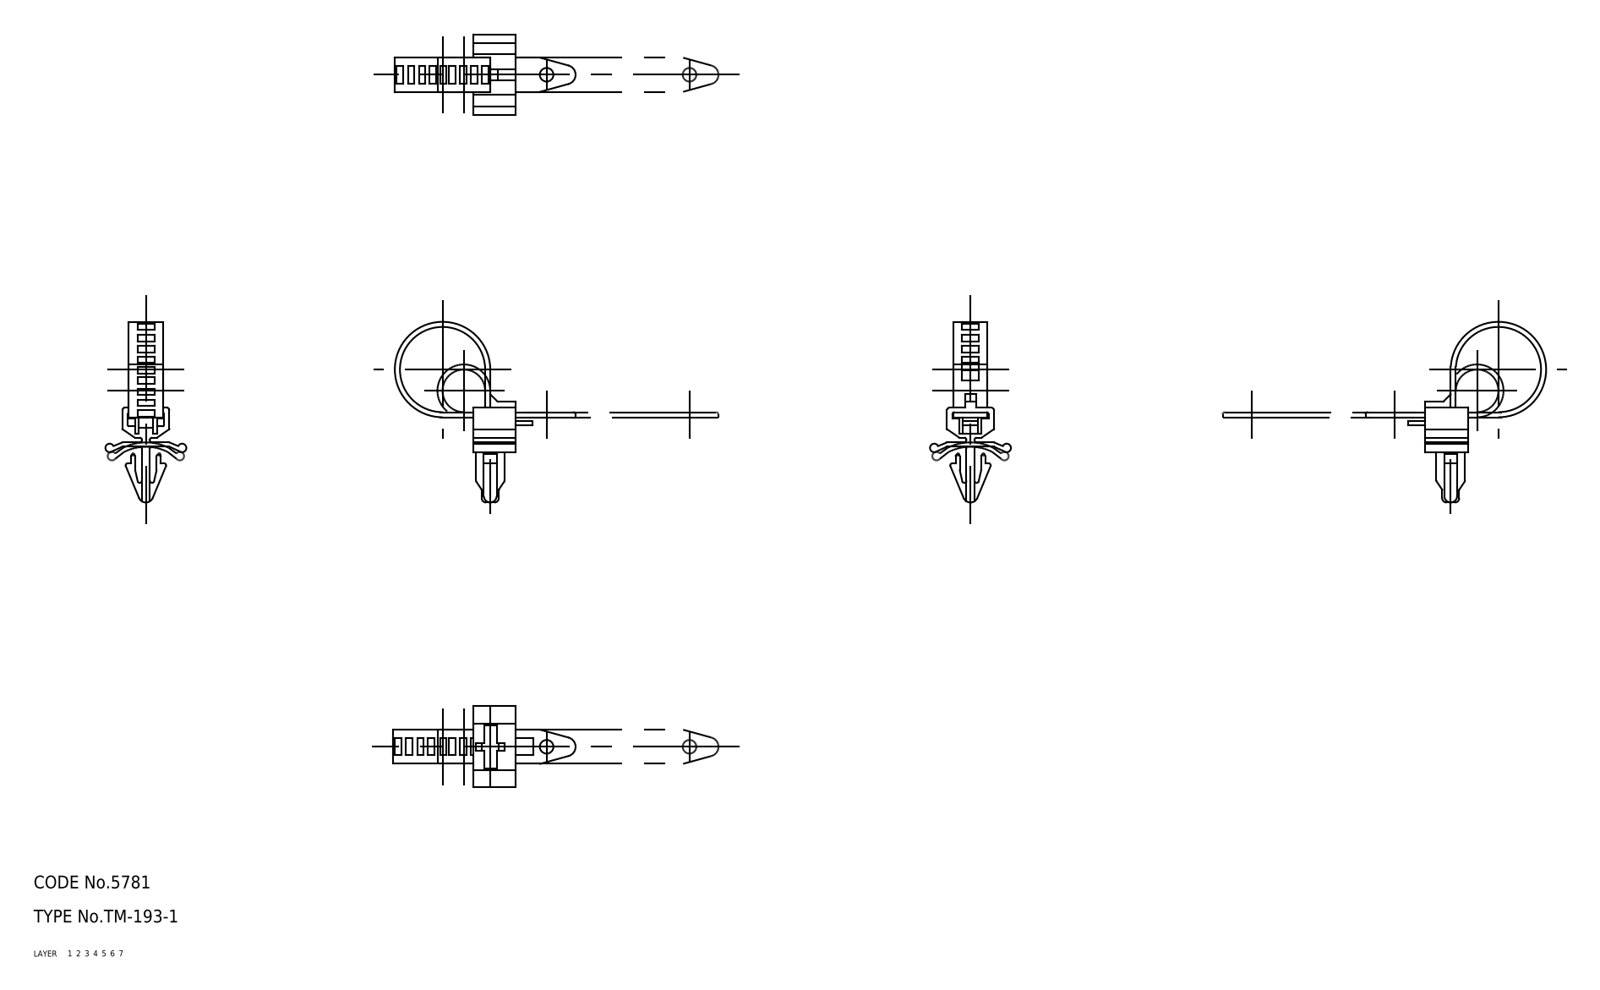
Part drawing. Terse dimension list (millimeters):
name: clip
written by: CADfix (AUTOMOTIVE_DESIGN)
unit: mm
bodies: 1 solid, 198 faces (0 planar, 0 cylindrical, 198 other)
size: 42.4 × 42.4 × 19
volume: 1 701 mm³; area: 3 113 mm²
